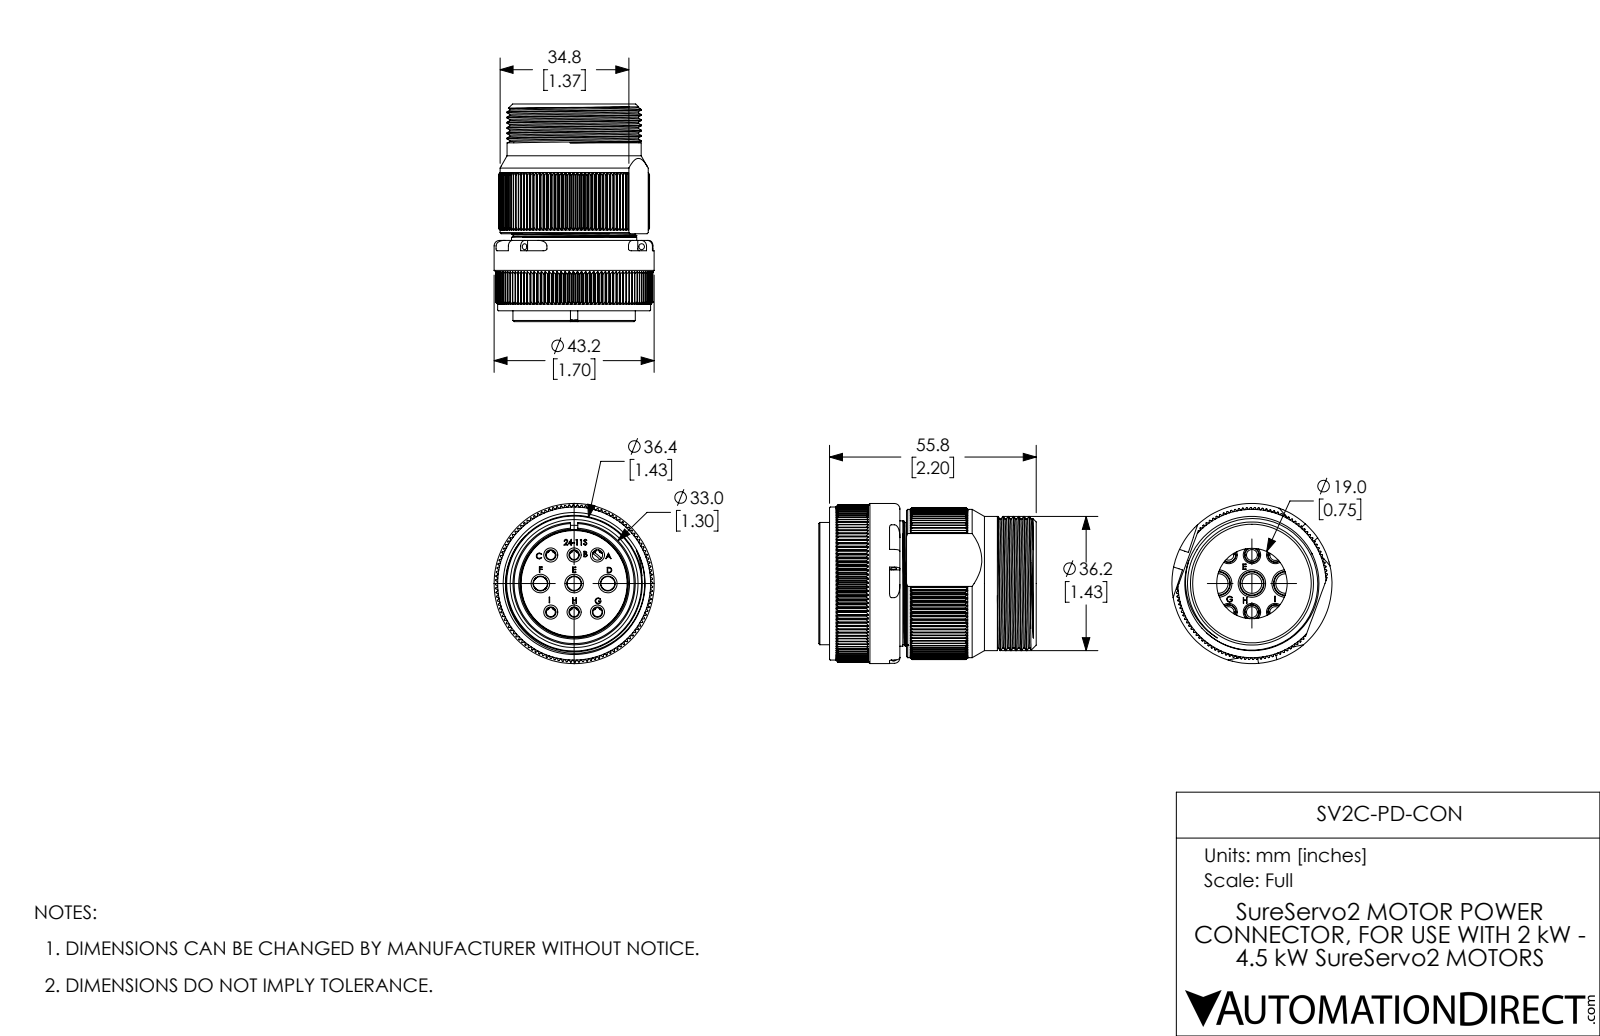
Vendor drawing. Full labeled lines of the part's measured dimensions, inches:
Part name (STEP PRODUCT): PD-CON r1 coord fXT b
STEP written by: SolidWorks 2017 (AUTOMOTIVE_DESIGN)
Units: inches
Bodies: 25 solids, 2535 faces (1101 planar, 835 cylindrical, 599 other)
Overall size (bounding box): 2.311 × 1.701 × 1.701
Volume: 2.787 in³ · Surface area: 71.62 in²
Round holes (diameter × count): ⌀0.157 ×9, ⌀0.11 ×6, ⌀0.185 ×6, ⌀0.201 ×6, ⌀0.22 ×6, ⌀0.096 ×5, ⌀0.116 ×5, ⌀0.063 ×3, ⌀0.148 ×3, ⌀0.198 ×3, ⌀0.209 ×3, ⌀0.252 ×3
Round bosses / shafts (diameter × count): ⌀0.189 ×5, ⌀0.15 ×5, ⌀0.297 ×3, ⌀0.246 ×3, ⌀0.23 ×3, ⌀0.223 ×3, ⌀0.215 ×3, ⌀1.701 ×1
Partial cylindrical surfaces — rounded edges, fillets, slot ends (radius × count): R0.016 ×24, R0.008 ×12, R0.01 ×12, R0.081 ×6, R0.02 ×5, R0.118 ×3, R0.033 ×1, R0.075 ×1
Main face-to-face distances: 0.063, 0.413, 0.476, 0.083, 0.846, 1.189, 0.016, 0.929, 0.657, 0.917
Hole centre spacings: 0.248, 0.322, 0.392, 0.469, 0.655, 0.678, 0.606, 0.303
